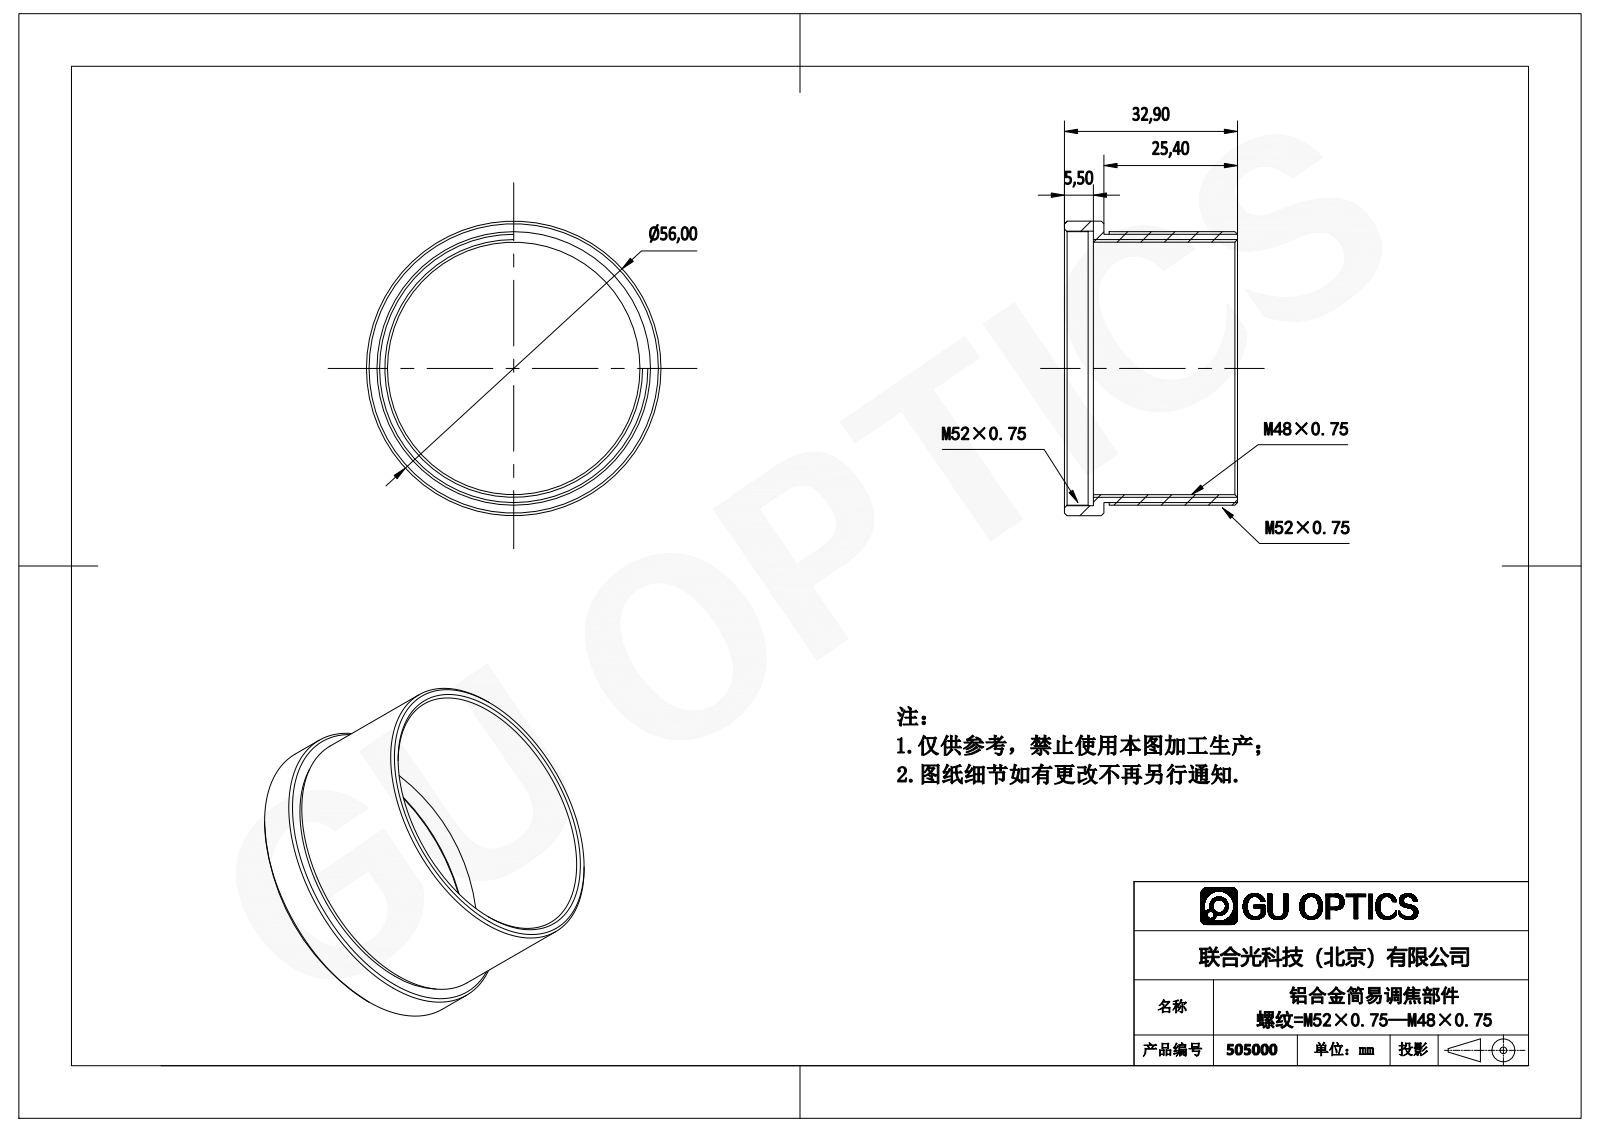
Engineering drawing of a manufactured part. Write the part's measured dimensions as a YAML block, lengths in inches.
part_name: "505000"
step_written_by: "SolidWorks 2016 (CONFIG_CONTROL_DESIGN)"
units: inches
bodies: {solids: 1, faces: 28, planar: 6, cylindrical: 12, other: 10}
overall_size: [2.205, 2.205, 1.295]
volume: 0.668
surface_area: 18.22
round_holes:
  - {diameter: 1.89, count: 1}
  - {diameter: 2.047, count: 1}
  - {diameter: 2.055, count: 1}
round_bosses_or_shafts:
  - {diameter: 2.205, count: 1}
  - {diameter: 2.008, count: 1}
face_to_face_distances: [0.079, 0.217, 0.295, 1.295, 1.079, 1, 0.039, 0.118, 0.335, 0.961]
